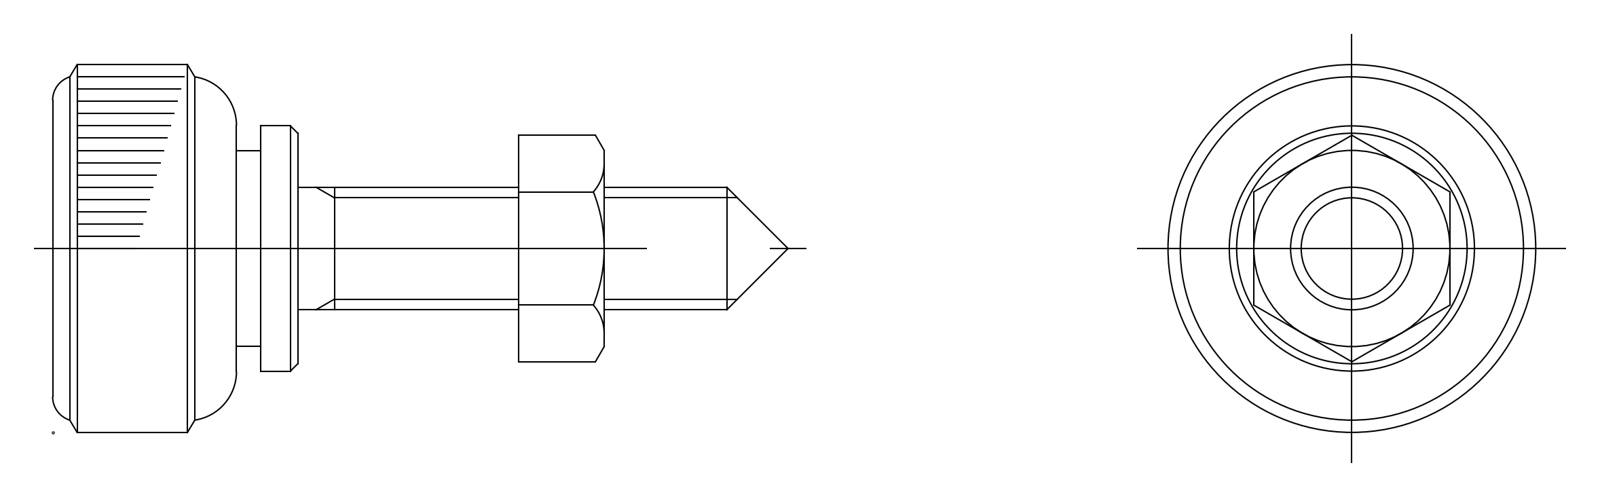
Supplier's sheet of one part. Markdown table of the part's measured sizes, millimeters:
| quantity | value |
| --- | --- |
| part name | THA_340SUS_15_5_Nツマミ; M5ナット |
| STEP written by | spGate 20.6.3 (****-****-****-****) (AUTOMOTIVE_DESIGN) |
| units | millimeters |
| bodies | 2 solids, 40 faces (12 planar, 10 cylindrical, 18 other) |
| overall size | 30 × 15 × 15 |
| volume | 1 892 mm³ |
| surface area | 1 272 mm² |
| round holes (diameter × count) | 5 × 1 |
| round bosses / shafts (diameter × count) | 15 × 1, 10 × 1, 8 × 1 |
| main face-to-face distances | 8, 10, 15.17, 5.17, 19.17, 9.17, 4, 7.5, 2.5, 7.67 |
